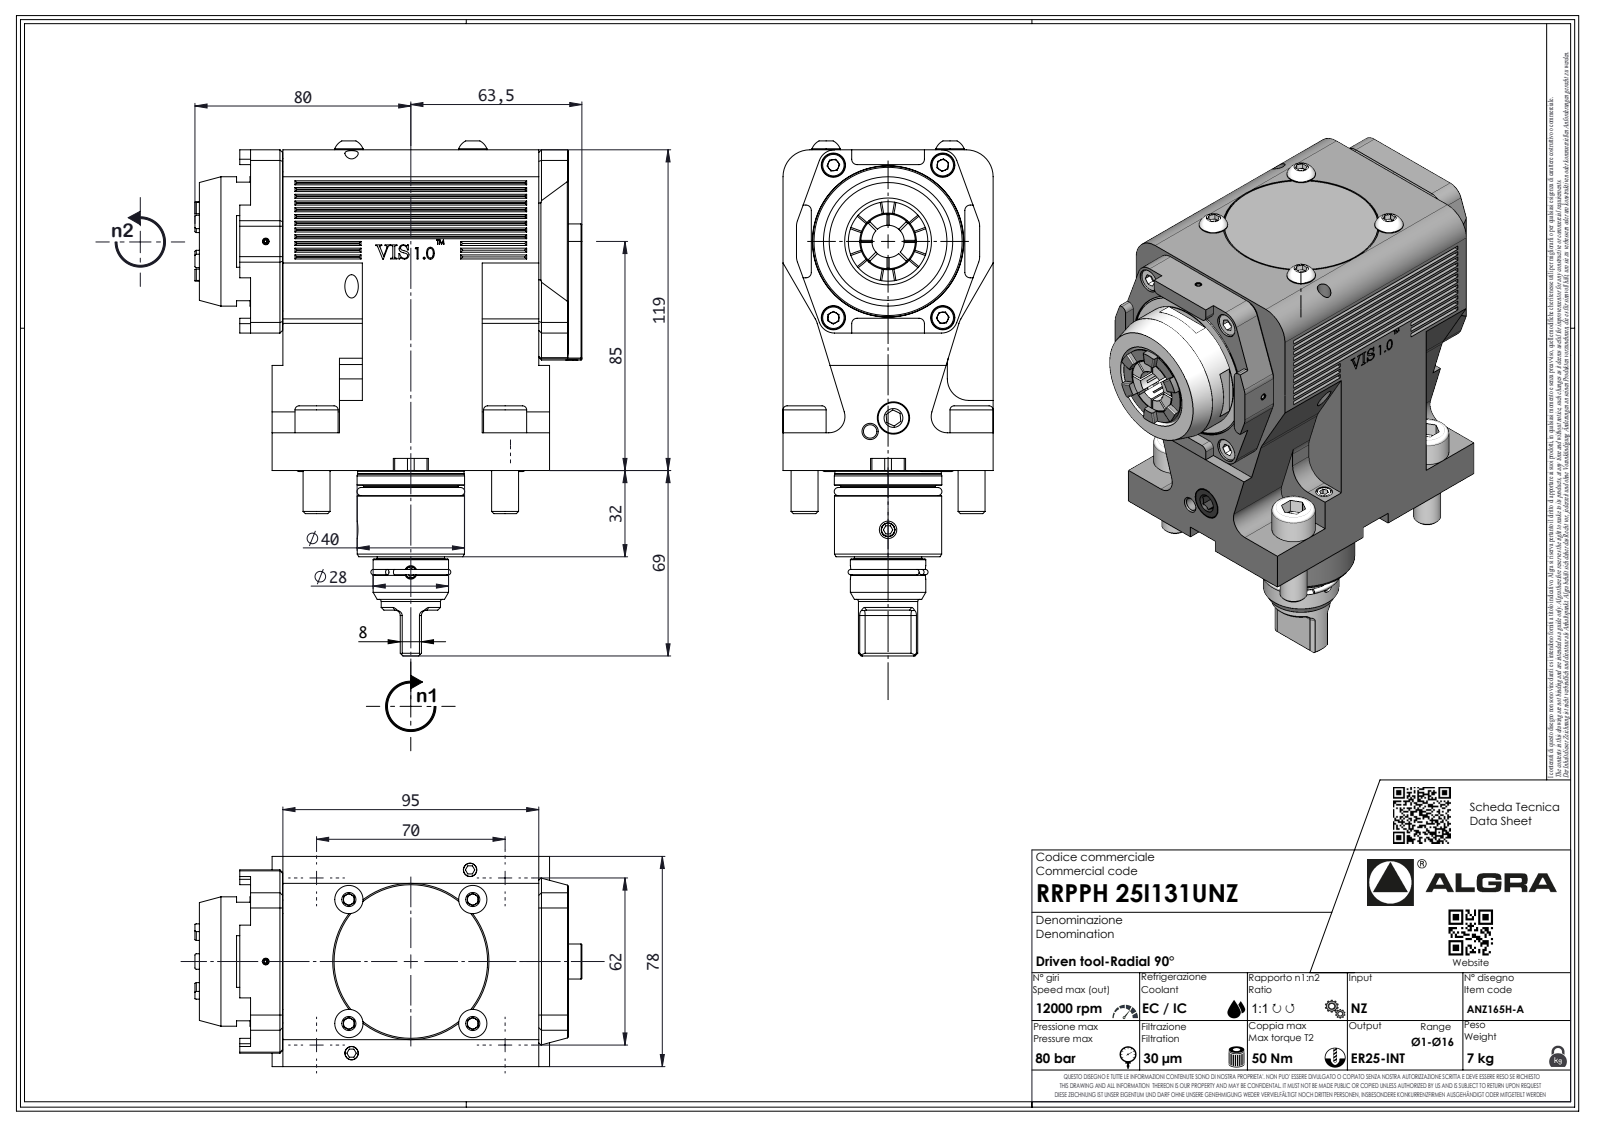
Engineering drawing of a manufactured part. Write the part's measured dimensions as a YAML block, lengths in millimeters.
part_name: "RRPPH25I131UNZ"
step_written_by: "SolidWorks 2023 (AUTOMOTIVE_DESIGN)"
units: millimeters
bodies: {solids: 1, faces: 652, planar: 390, cylindrical: 131, other: 131}
overall_size: [187.8, 143.65, 78]
volume: 998532
surface_area: 87751
round_holes:
  - {diameter: 2.1, count: 1}
  - {diameter: 6, count: 1}
round_bosses_or_shafts:
  - {diameter: 16, count: 4}
  - {diameter: 10, count: 4}
  - {diameter: 48, count: 1}
  - {diameter: 39.9, count: 1}
  - {diameter: 39.8, count: 1}
  - {diameter: 39.5, count: 1}
  - {diameter: 35.1, count: 1}
  - {diameter: 35, count: 1}
partial_cylinders:
  - {radius: 5, count: 16}
  - {radius: 2, count: 14}
  - {radius: 6, count: 10}
  - {radius: 0.33, count: 7}
  - {radius: 0.52, count: 7}
  - {radius: 3.7, count: 7}
  - {radius: 8, count: 6}
  - {radius: 35, count: 6}
face_to_face_distances: [78, 119, 4, 12, 99, 106, 25, 106.1, 111, 21]
